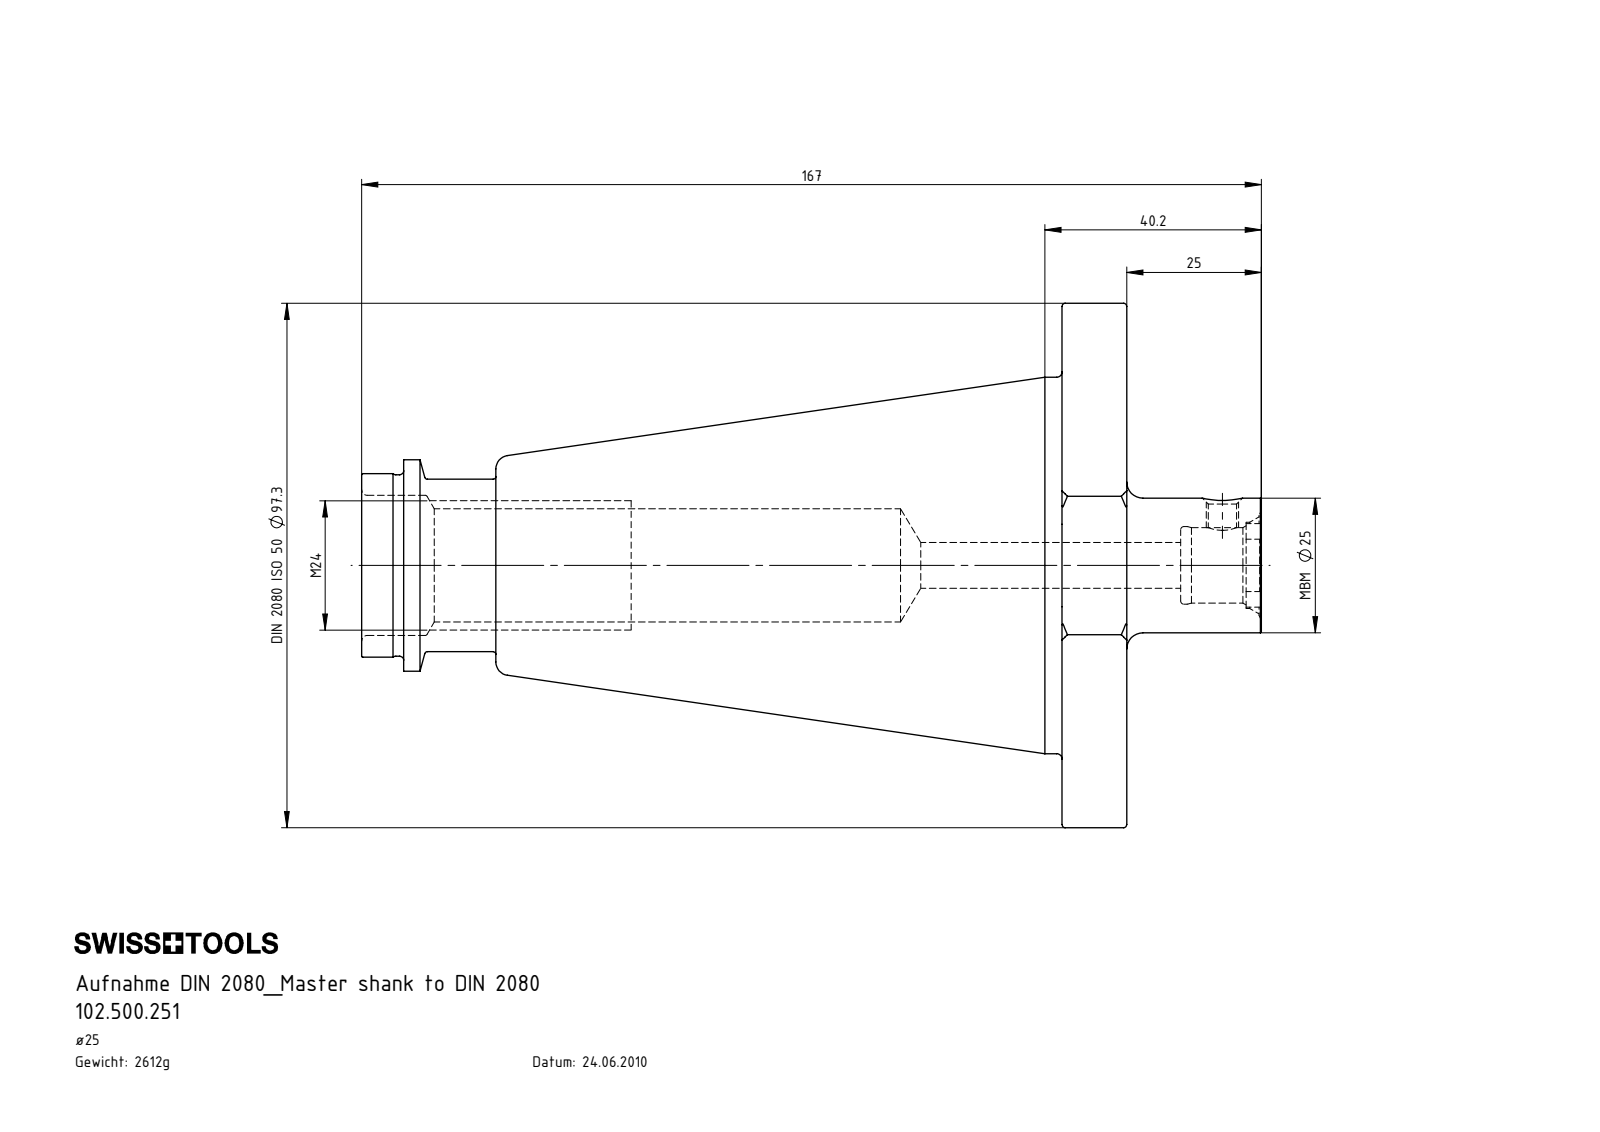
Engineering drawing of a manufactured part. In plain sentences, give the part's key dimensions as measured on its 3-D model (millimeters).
The part is named "102.500.251". Its 3-D file was written by "SolidWorks 2017 (CONFIG_CONTROL_DESIGN)". It is 1 solid with 128 faces: 31 planar, 49 cylindrical and 48 other. Overall it measures 167 by 97.3 by 93.84 millimeters. Its volume is 332 738 cubic millimeters and its surface area 47 079 square millimeters. Round holes: 1 of diameter 5.25, 1 of diameter 8.5, 1 of diameter 14, 1 of diameter 14.4, 1 of diameter 21, 1 of diameter 26. Round bosses or shafts: 1 of diameter 97.3, 1 of diameter 69.85, 1 of diameter 39.24, 1 of diameter 34.05, 1 of diameter 33.65, 1 of diameter 32, 1 of diameter 25. Partial cylindrical surfaces (rounded edges, fillets, slot ends): 12 of radius 2, 4 of radius 2.7, 1 of radius 8, 1 of radius 9.53. The main face-to-face distances are 12, 130, 142, 70.2, 7.8, 122.2, 134.2, 25.7, 24.9, 17.1.
